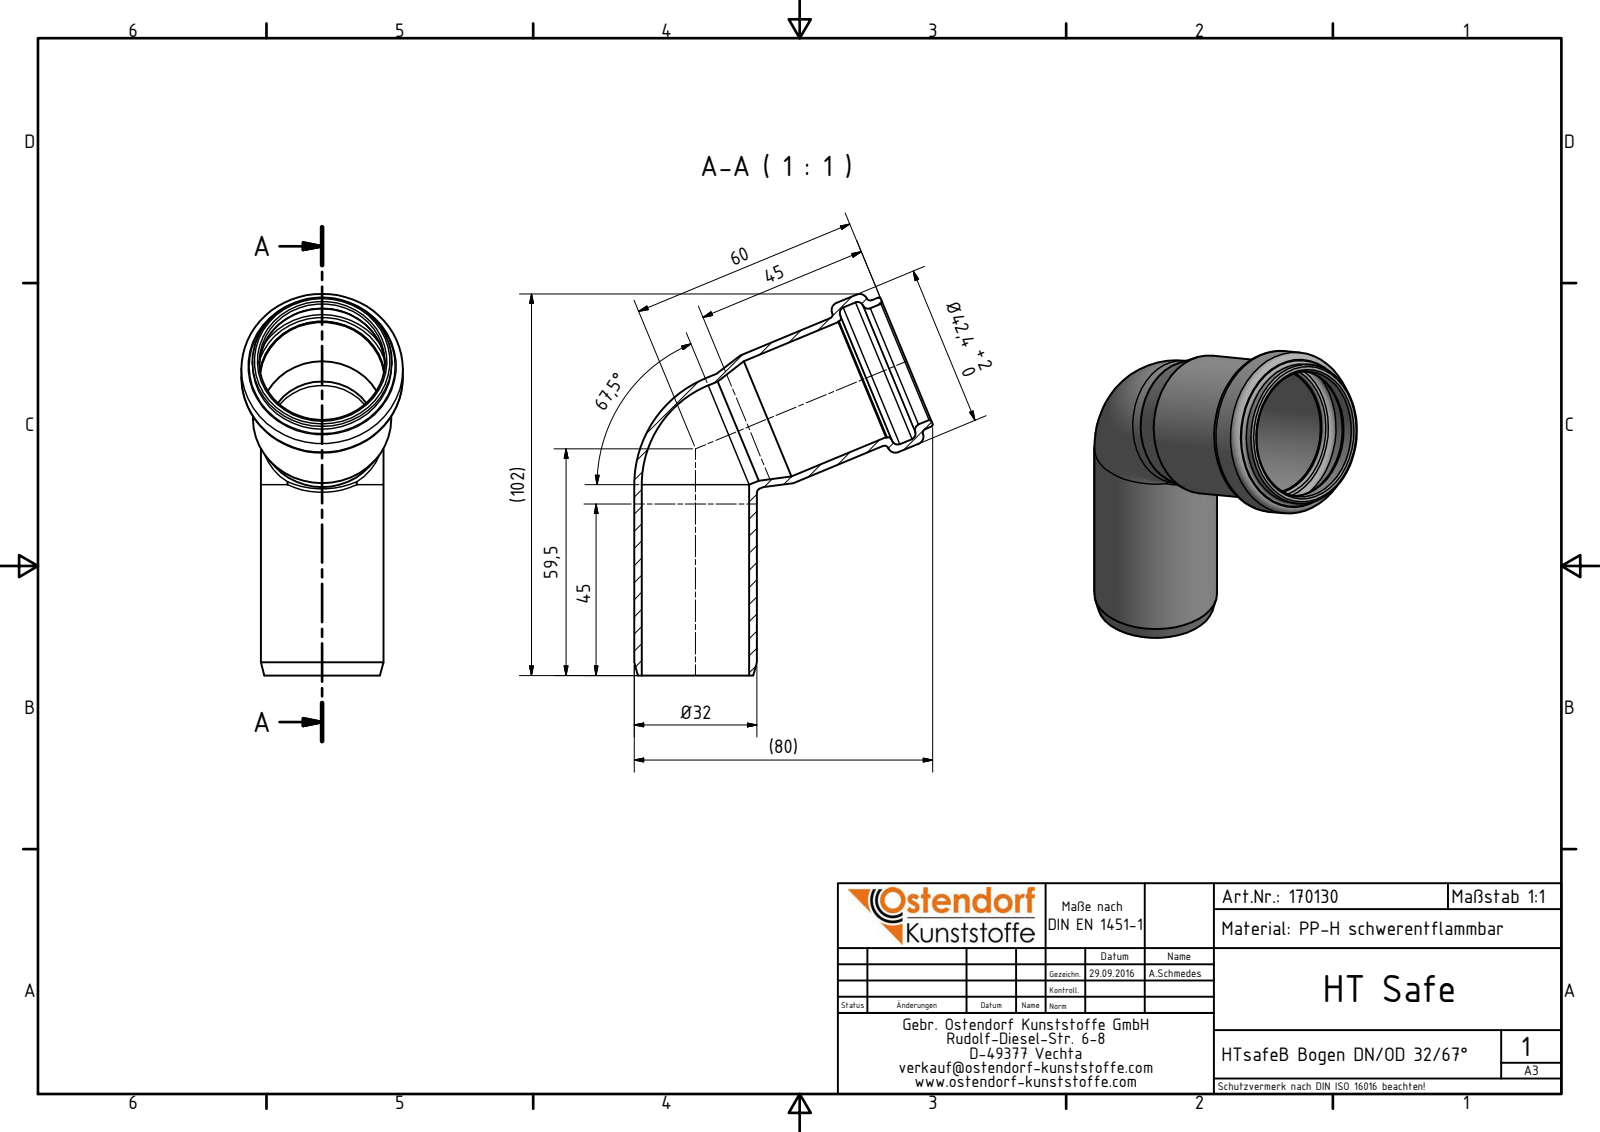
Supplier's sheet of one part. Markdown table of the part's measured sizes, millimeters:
| quantity | value |
| --- | --- |
| part name | 170130 HTsafeB DN_OD 32_67° |
| STEP written by | Autodesk Inventor 2016 (AUTOMOTIVE_DESIGN) |
| units | millimeters |
| bodies | 1 solid, 34 faces (3 planar, 11 cylindrical, 20 other) |
| overall size | 100.15 × 78.38 × 42.4 |
| volume | 23 013 mm³ |
| surface area | 24 867 mm² |
| round holes (diameter × count) | 28.2 × 2, 33 × 2, 32.7 × 1, 38.8 × 1 |
| round bosses / shafts (diameter × count) | 32.2 × 2, 42.4 × 1, 36.6 × 1, 36.3 × 1 |
| main face-to-face distances | 12.63 |
